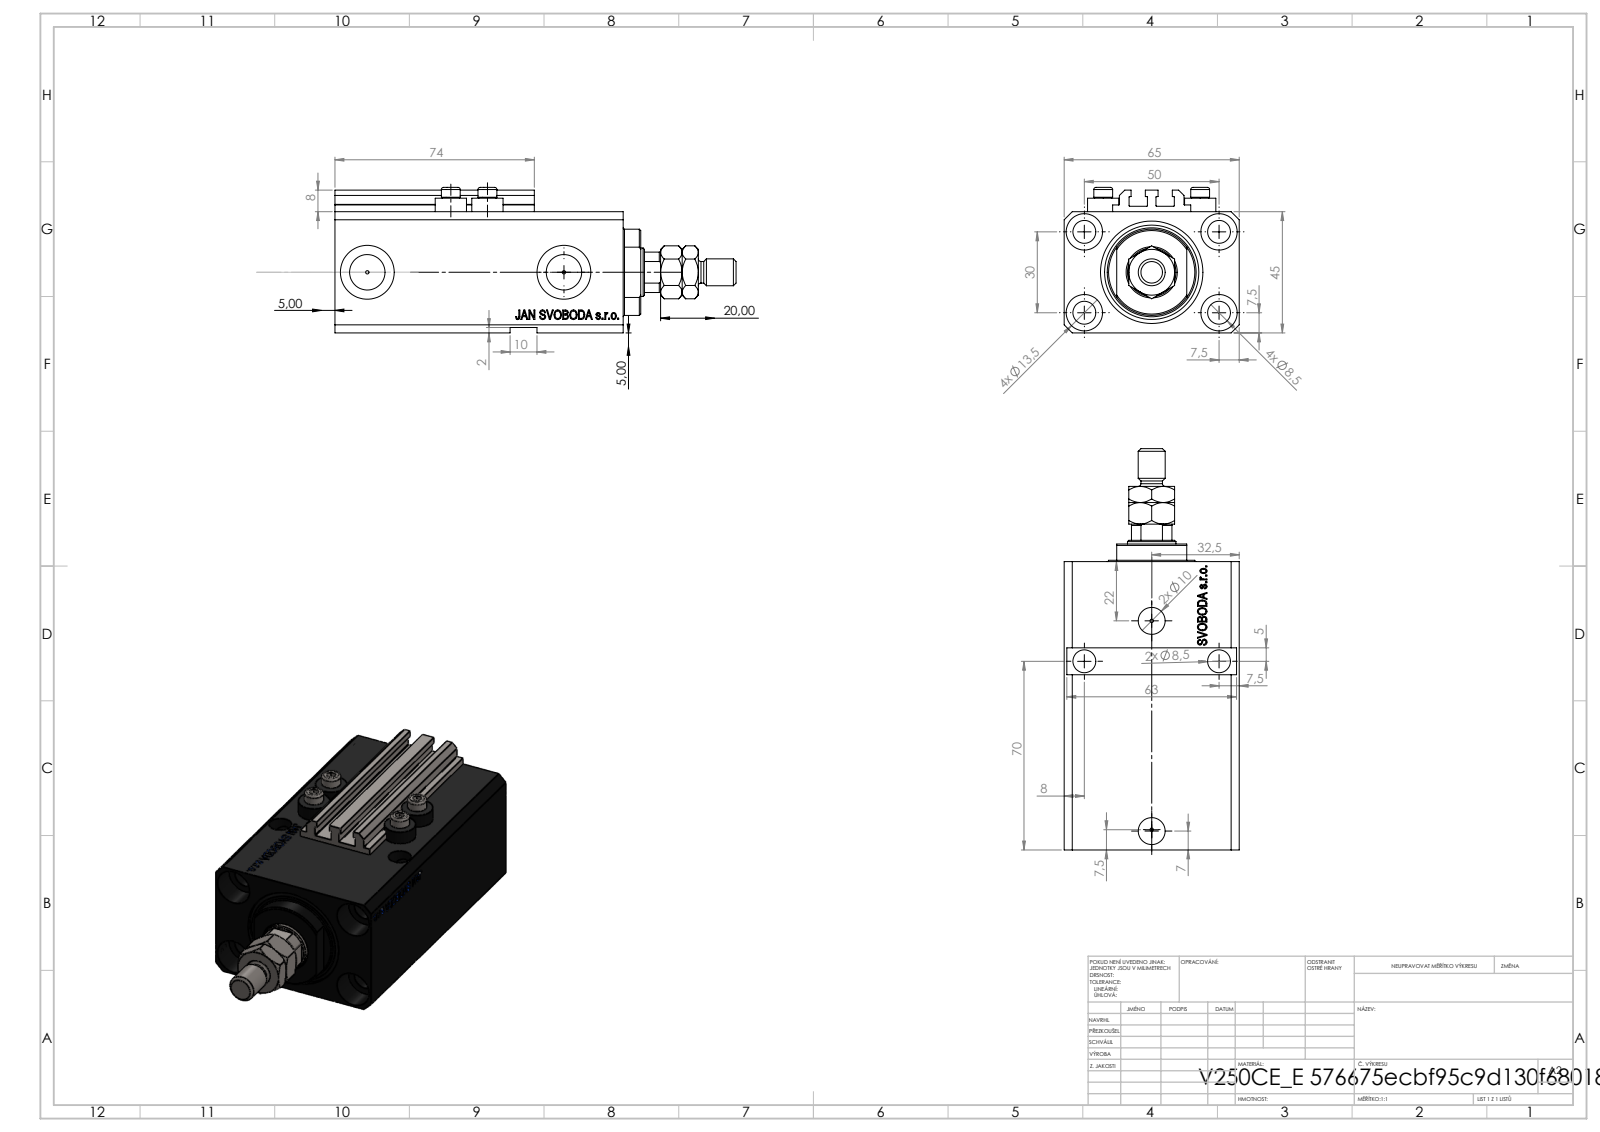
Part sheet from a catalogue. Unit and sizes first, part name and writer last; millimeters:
Units: millimetres
Overall size (bounding box): 149 × 65 × 54
Round holes (diameter × count): ⌀8.5 ×9, ⌀1.25 ×4, ⌀4 ×4, ⌀13.5 ×4, ⌀10 ×2, ⌀13.16 ×2, ⌀20 ×2, ⌀18 ×1, ⌀25 ×1, ⌀38 ×1
Round bosses / shafts (diameter × count): ⌀11.6 ×4, ⌀7 ×4, ⌀10 ×1, ⌀8 ×1
Partial cylindrical surfaces — rounded edges, fillets, slot ends (radius × count): R0.2 ×10, R8.5 ×1, R16 ×1
Main face-to-face distances: 45, 65, 14, 93, 2, 47, 107, 6.9, 20.5, 2.5
Hole centre spacings: 29.15, 50, 13.6, 14.76, 15.12, 27.51, 27.89, 30
Volume: 277 886 mm³ · Surface area: 78 614 mm²
Bodies: 9 solids, 1136 faces (526 planar, 150 cylindrical, 460 other)
Part name (STEP PRODUCT): V250CE_VC_E; V250CE_E_Body; V250CE_C_VCP; MTA (+1 more)
STEP written by: SolidWorks 2019 (CONFIG_CONTROL_DESIGN)
